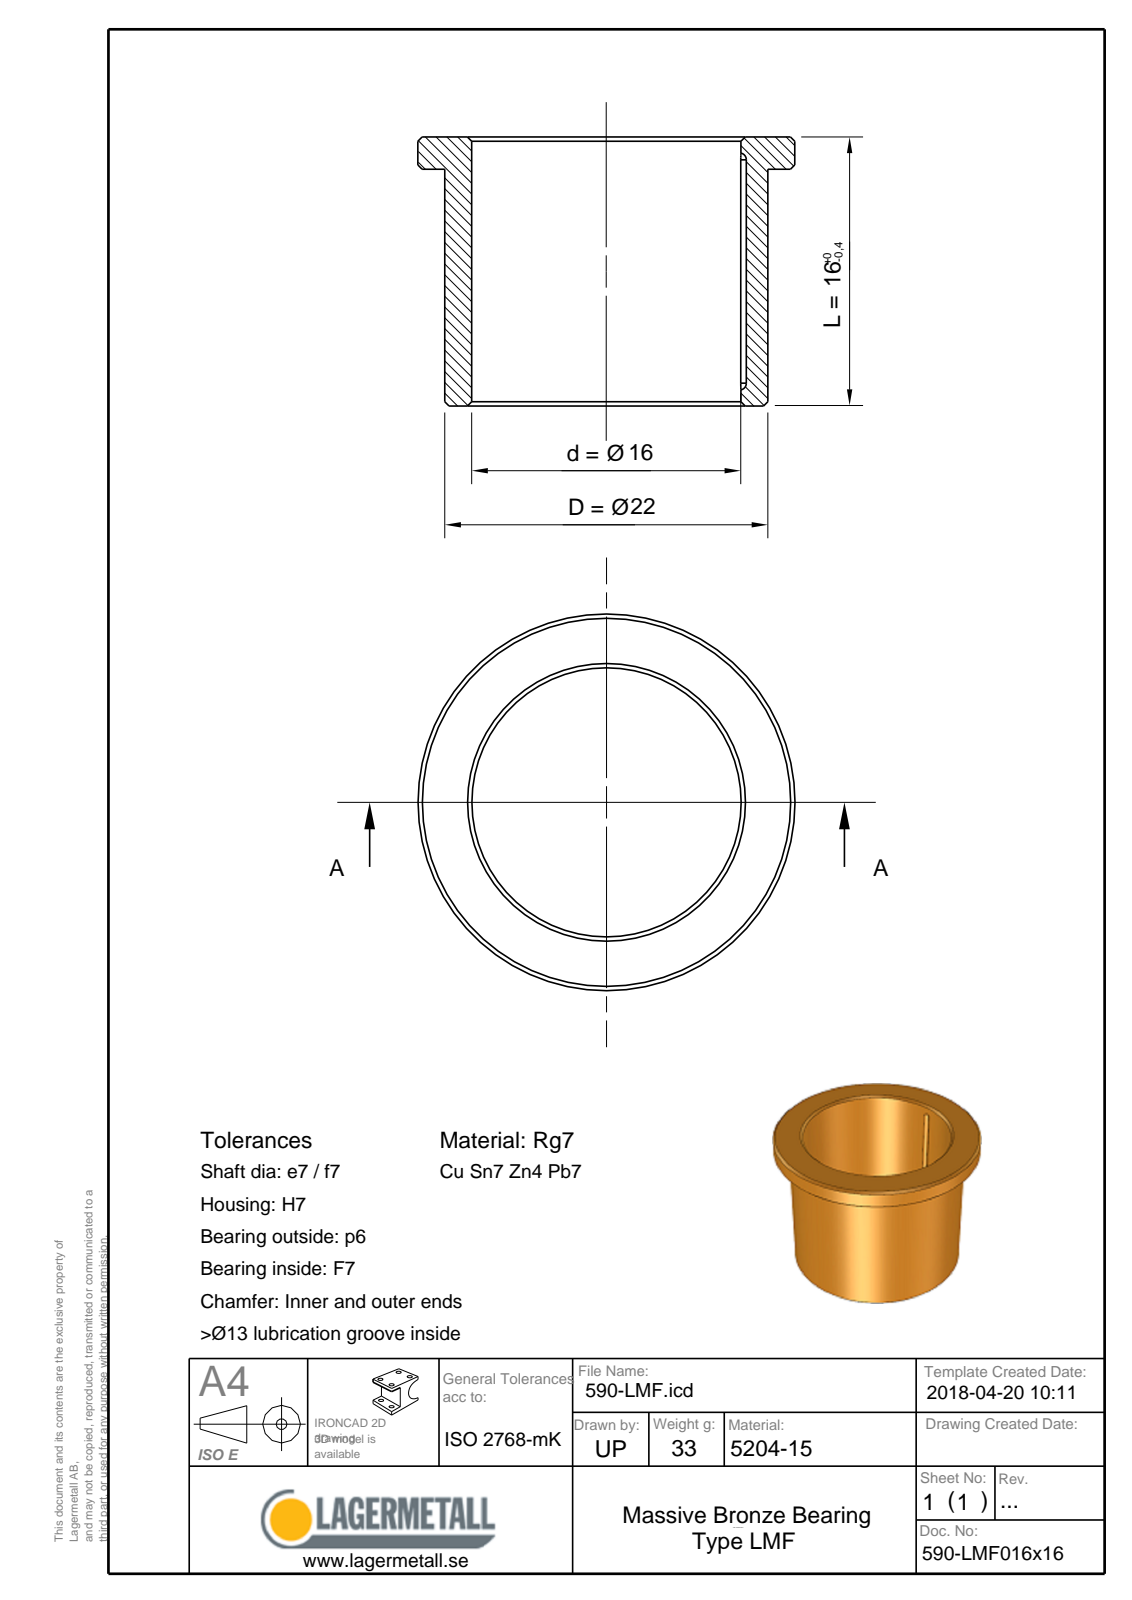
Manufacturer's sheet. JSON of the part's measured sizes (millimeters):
{"part_name": "590-LMF016x16", "step_written_by": "Spatial InterOp 3D (CONFIG_CONTROL_DESIGN)", "units": "millimeters", "bodies": {"solids": 1, "faces": 18, "planar": 5, "cylindrical": 6, "other": 7}, "overall_size": [28, 28, 16], "volume_mm3": 3752, "surface_area_mm2": 2728, "round_holes": [[16, 1]], "round_bosses_or_shafts": [[28, 1], [22, 1]], "partial_cylinders_radius": [[0.75, 3]], "face_to_face_distances": [4, 12, 16, 1.5]}
